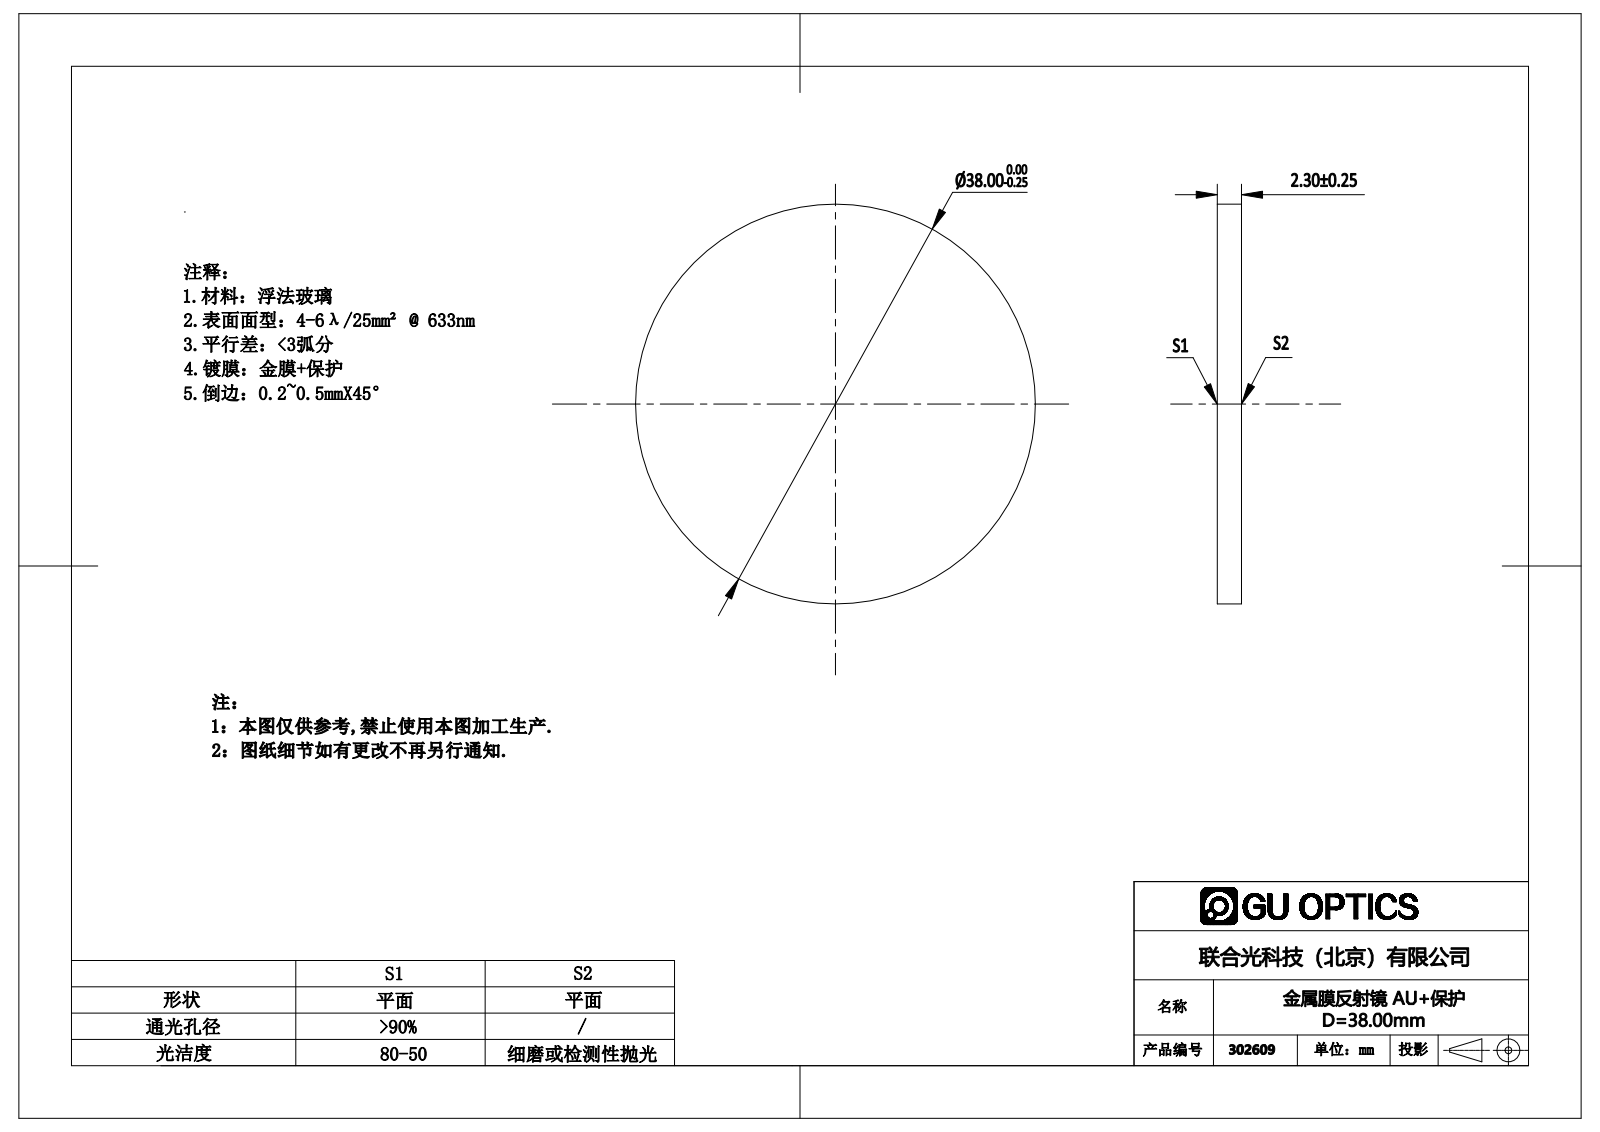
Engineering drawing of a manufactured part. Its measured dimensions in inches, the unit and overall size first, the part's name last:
Units: inches
Overall size (bounding box): 1.496 × 1.496 × 0.091
Round bosses / shafts (diameter × count): ⌀1.496 ×1
Main face-to-face distances: 0.091
Volume: 0.159 in³ · Surface area: 3.942 in²
Bodies: 1 solid, 4 faces (2 planar, 2 cylindrical, 0 other)
Part name (STEP PRODUCT): 302522
STEP written by: SolidWorks 2016 (AUTOMOTIVE_DESIGN)
